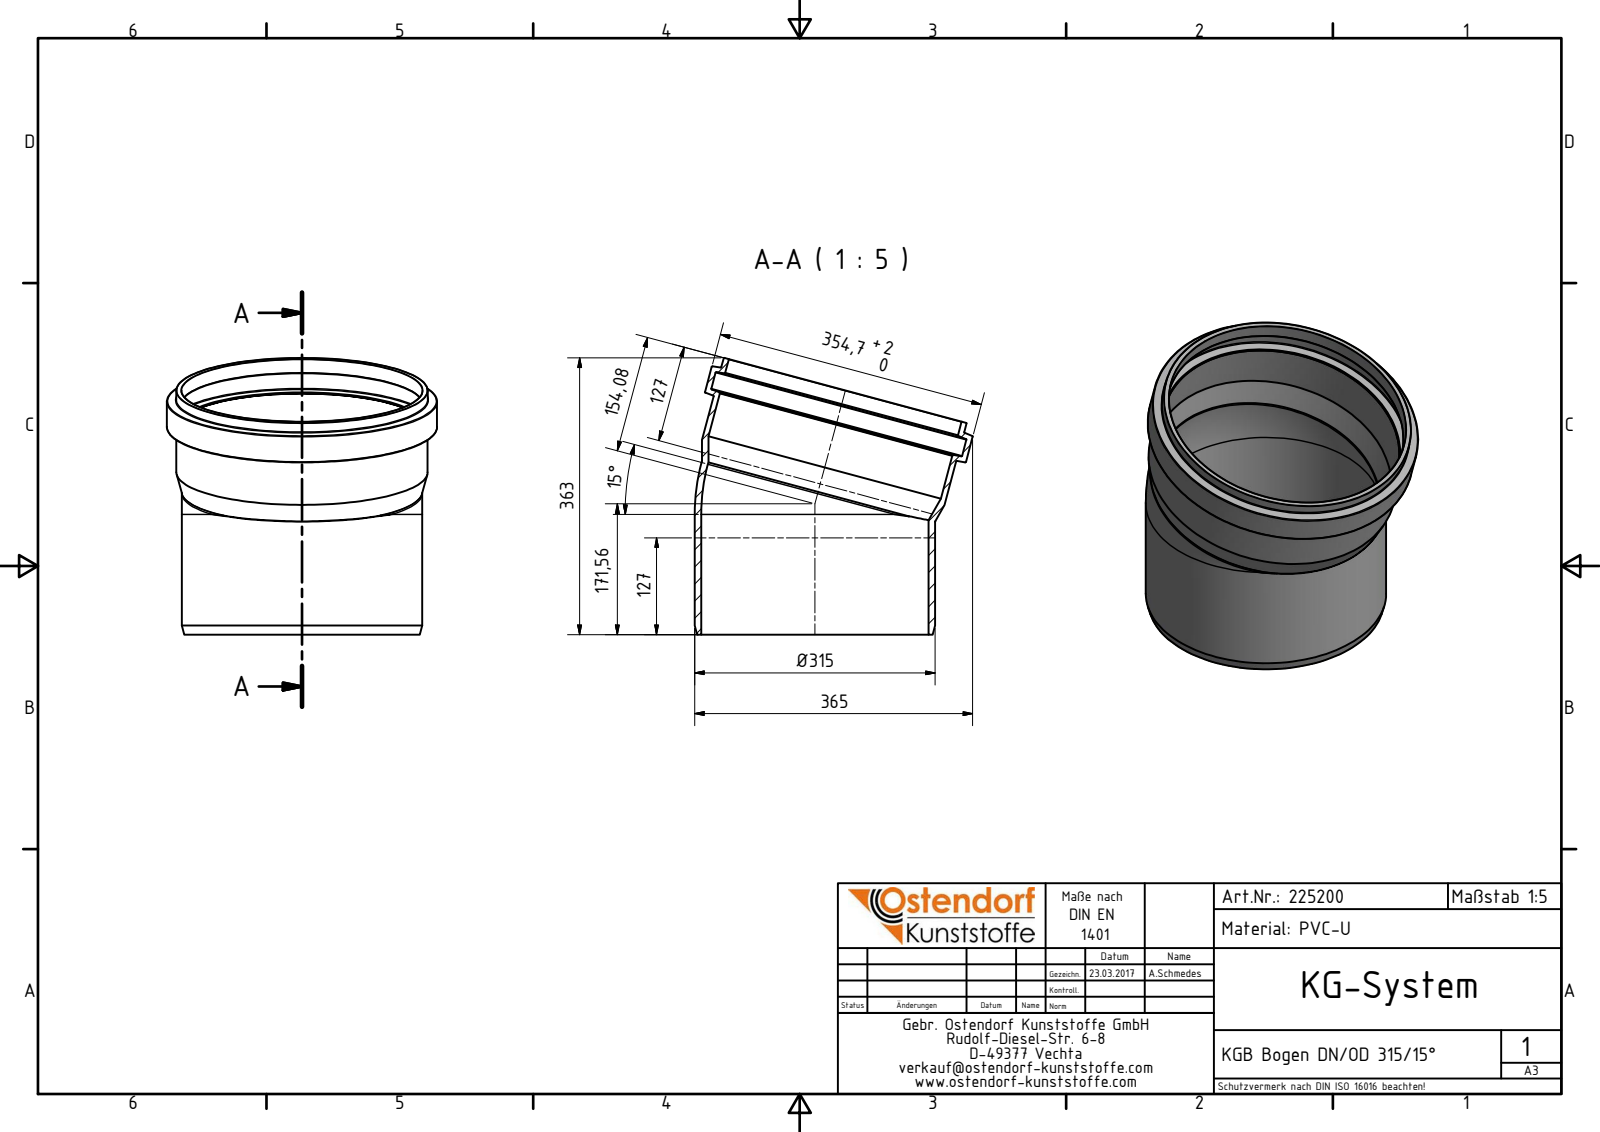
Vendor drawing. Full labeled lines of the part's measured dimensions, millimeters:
Part name (STEP PRODUCT): 225200 KGB Bogen DN_OD 315_15°
STEP written by: Autodesk Inventor 2016 (AUTOMOTIVE_DESIGN)
Units: millimetres
Bodies: 1 solid, 39 faces (3 planar, 11 cylindrical, 25 other)
Overall size (bounding box): 365 × 363 × 354.7
Volume: 2 748 000 mm³ · Surface area: 703 236 mm²
Round holes (diameter × count): ⌀298.2 ×2, ⌀316.3 ×2, ⌀316 ×1, ⌀340.9 ×1
Round bosses / shafts (diameter × count): ⌀354.7 ×1, ⌀330.1 ×1, ⌀329.8 ×1, ⌀315.6 ×1
Partial cylindrical surfaces — rounded edges, fillets, slot ends (radius × count): R157.8 ×1
Main face-to-face distances: 46.56
